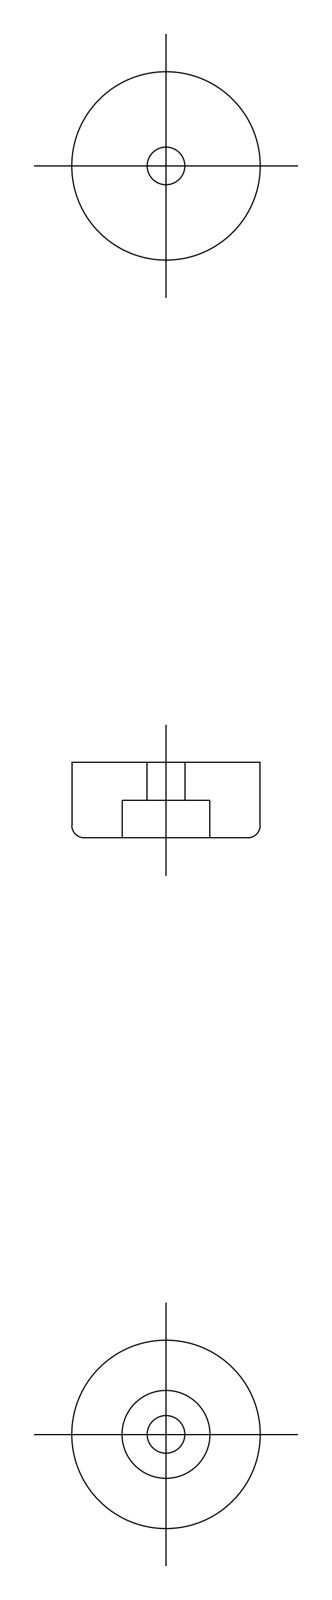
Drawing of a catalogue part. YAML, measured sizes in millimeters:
part_name: "washer; rubber foot; SK_156_8781_36"
step_written_by: "CADfix (AUTOMOTIVE_DESIGN)"
units: millimeters
bodies: {solids: 2, faces: 20, planar: 0, cylindrical: 0, other: 20}
overall_size: [15, 15, 6]
volume: 916
surface_area: 888
